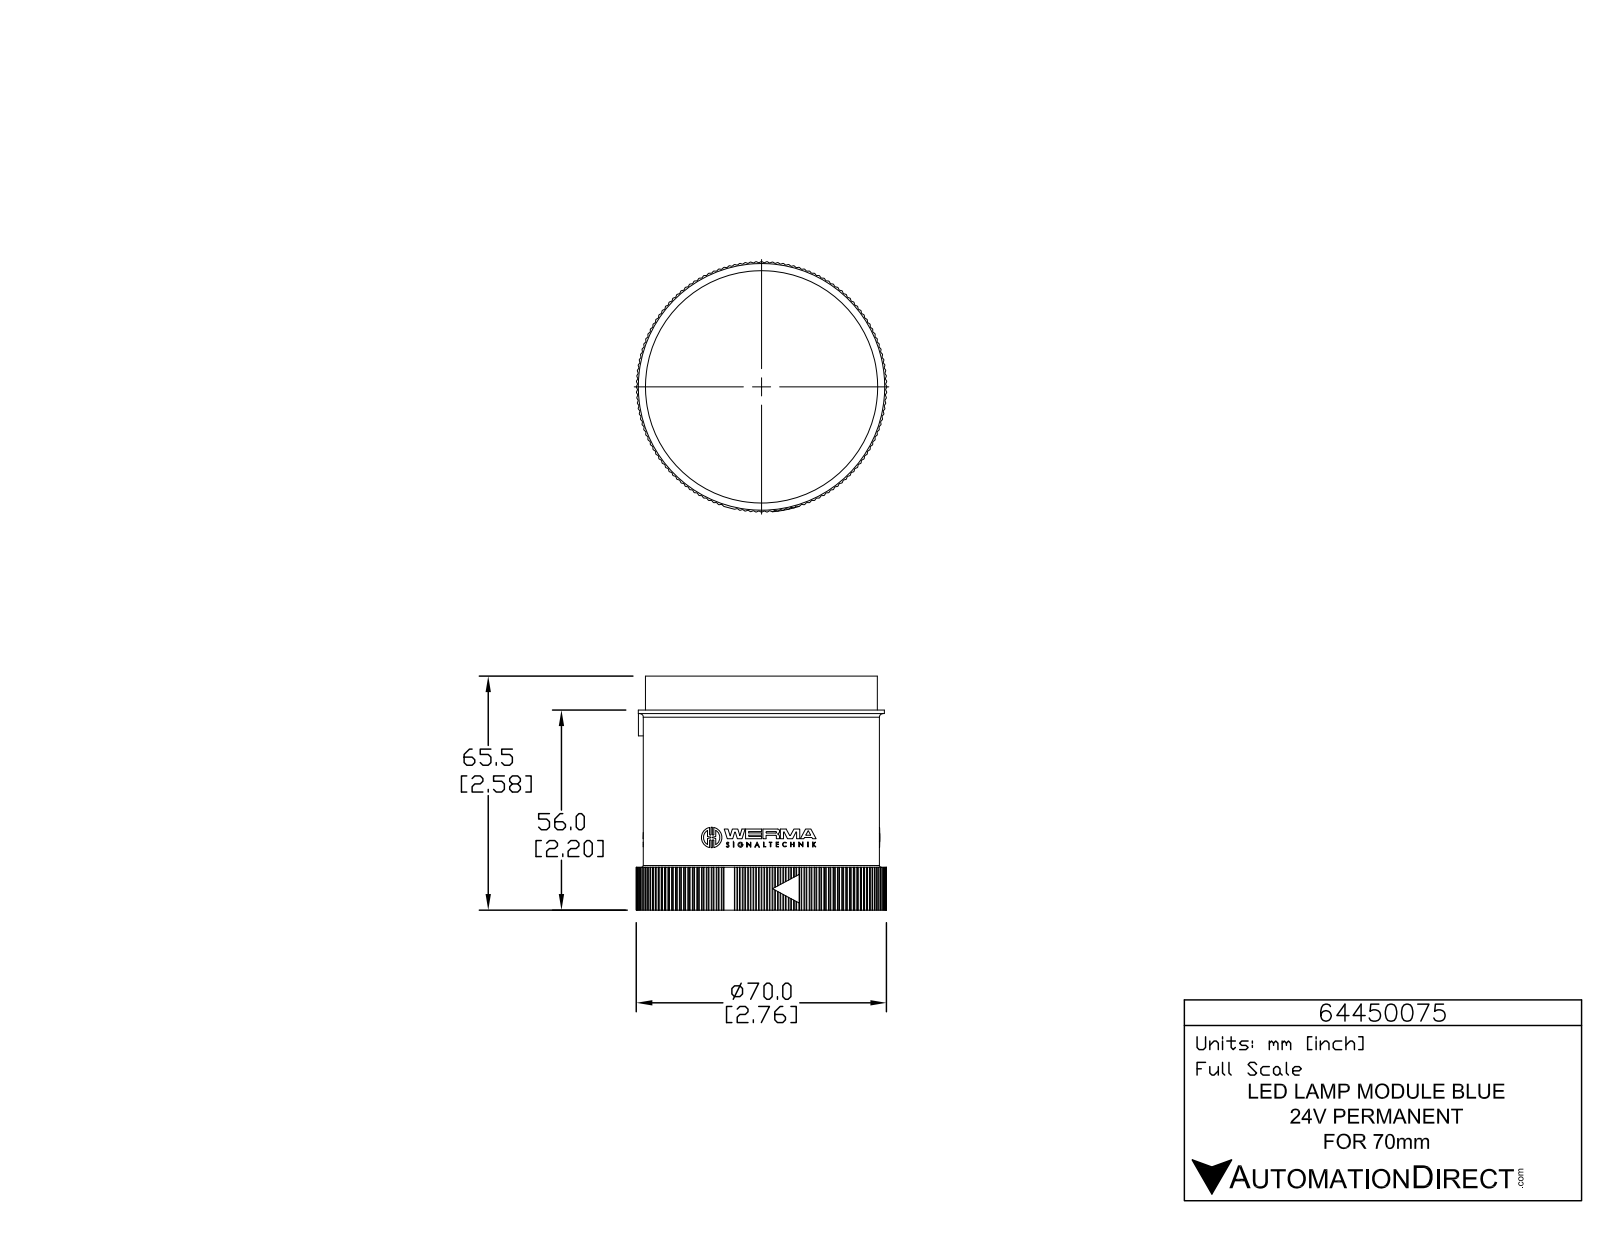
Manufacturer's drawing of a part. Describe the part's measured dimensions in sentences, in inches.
The part is named "64450075". Its 3-D file was written by "SolidWorks 2015 (AUTOMOTIVE_DESIGN)". It is 1 solid with 1400 faces: 832 planar, 563 cylindrical and 5 other. Overall it measures 2.762 by 2.762 by 2.579 inches. Its volume is 12.02 cubic inches and its surface area 37.48 square inches. Round holes: 3 of diameter 0.039, 1 of diameter 2.575. Round bosses or shafts: 3 of diameter 0.226, 3 of diameter 0.056, 1 of diameter 2.717, 1 of diameter 2.606, 1 of diameter 2.559. Partial cylindrical surfaces (rounded edges, fillets, slot ends): 285 of radius 0.008, 6 of radius 0.008, 6 of radius 0.008, 6 of radius 0.008, 6 of radius 0.131, 3 of radius 0.004, 3 of radius 0.005, 3 of radius 0.008. The main face-to-face distances are 2.201, 2.451, 0.378, 2.579, 2.205, 1.827, 0.374, 2.452, 0.472, 0.094.
